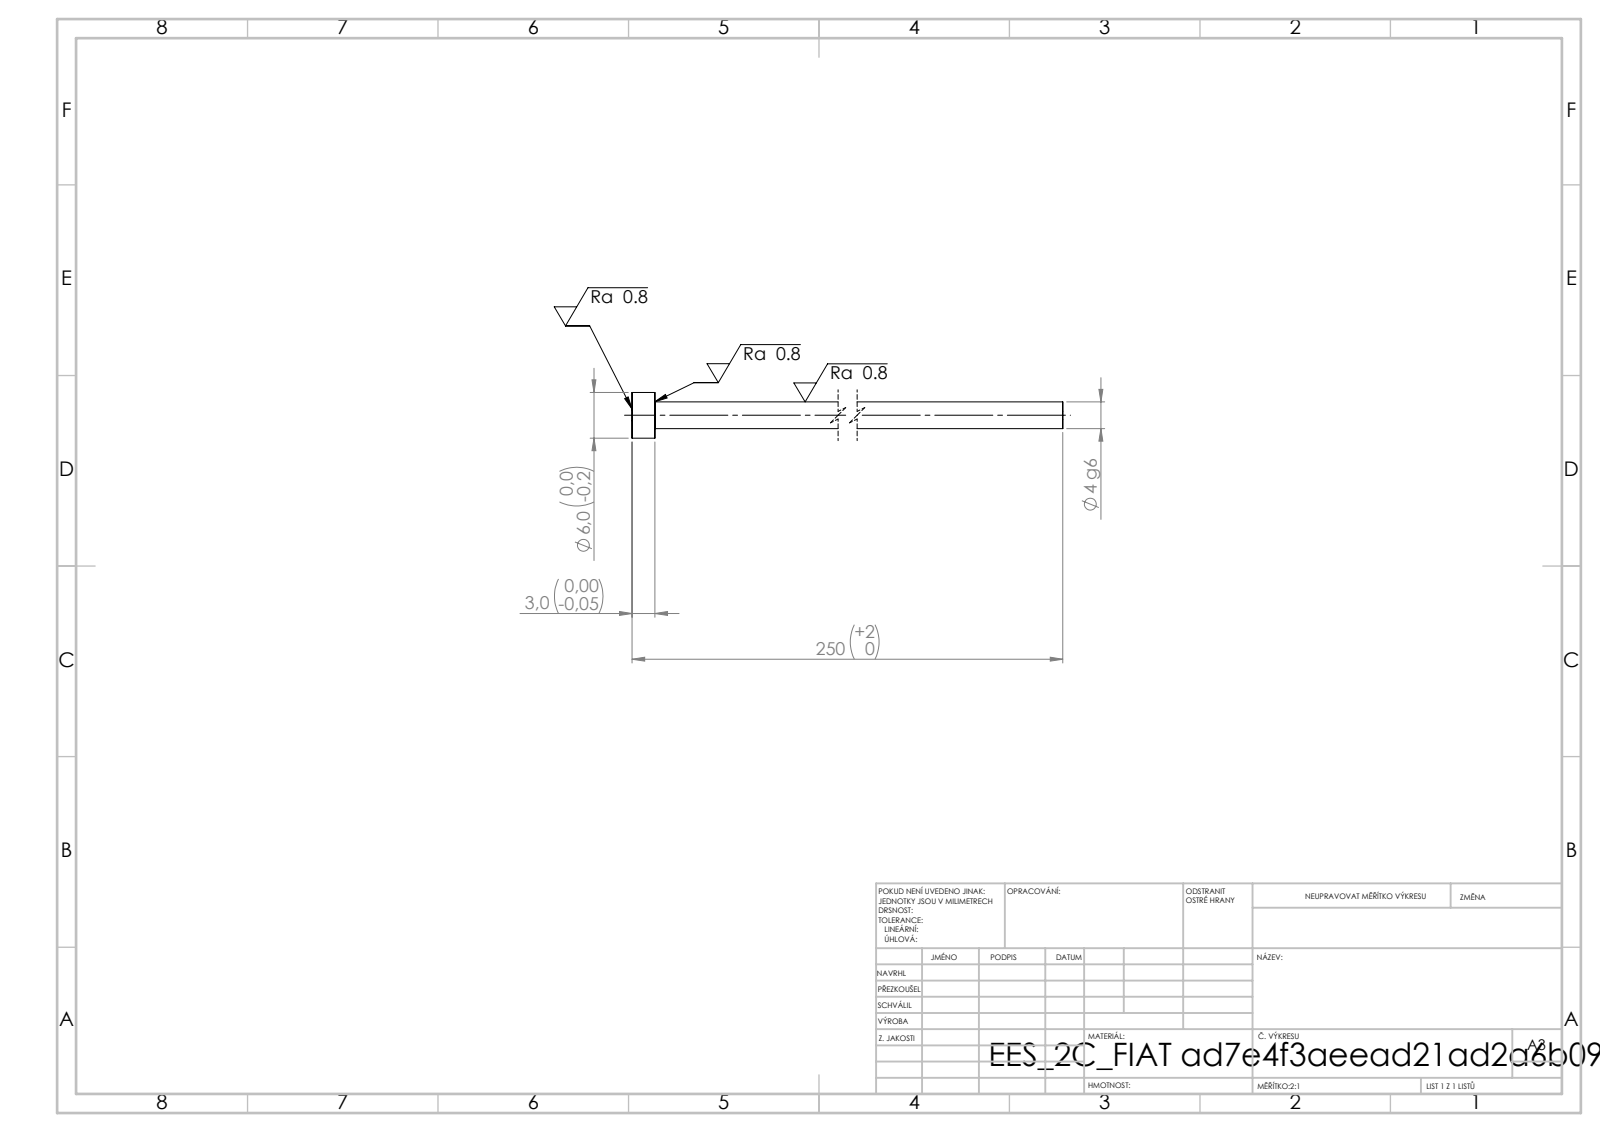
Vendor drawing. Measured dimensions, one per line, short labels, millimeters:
written by: SolidWorks 2019 (CONFIG_CONTROL_DESIGN)
unit: mm
bodies: 1 solid, 7 faces (3 planar, 4 cylindrical, 0 other)
size: 250 × 6 × 6
volume: 2 461 mm³; area: 2 829 mm²
bosses: 1× ⌀6, 1× ⌀3.5
face distances: 3, 250, 247
